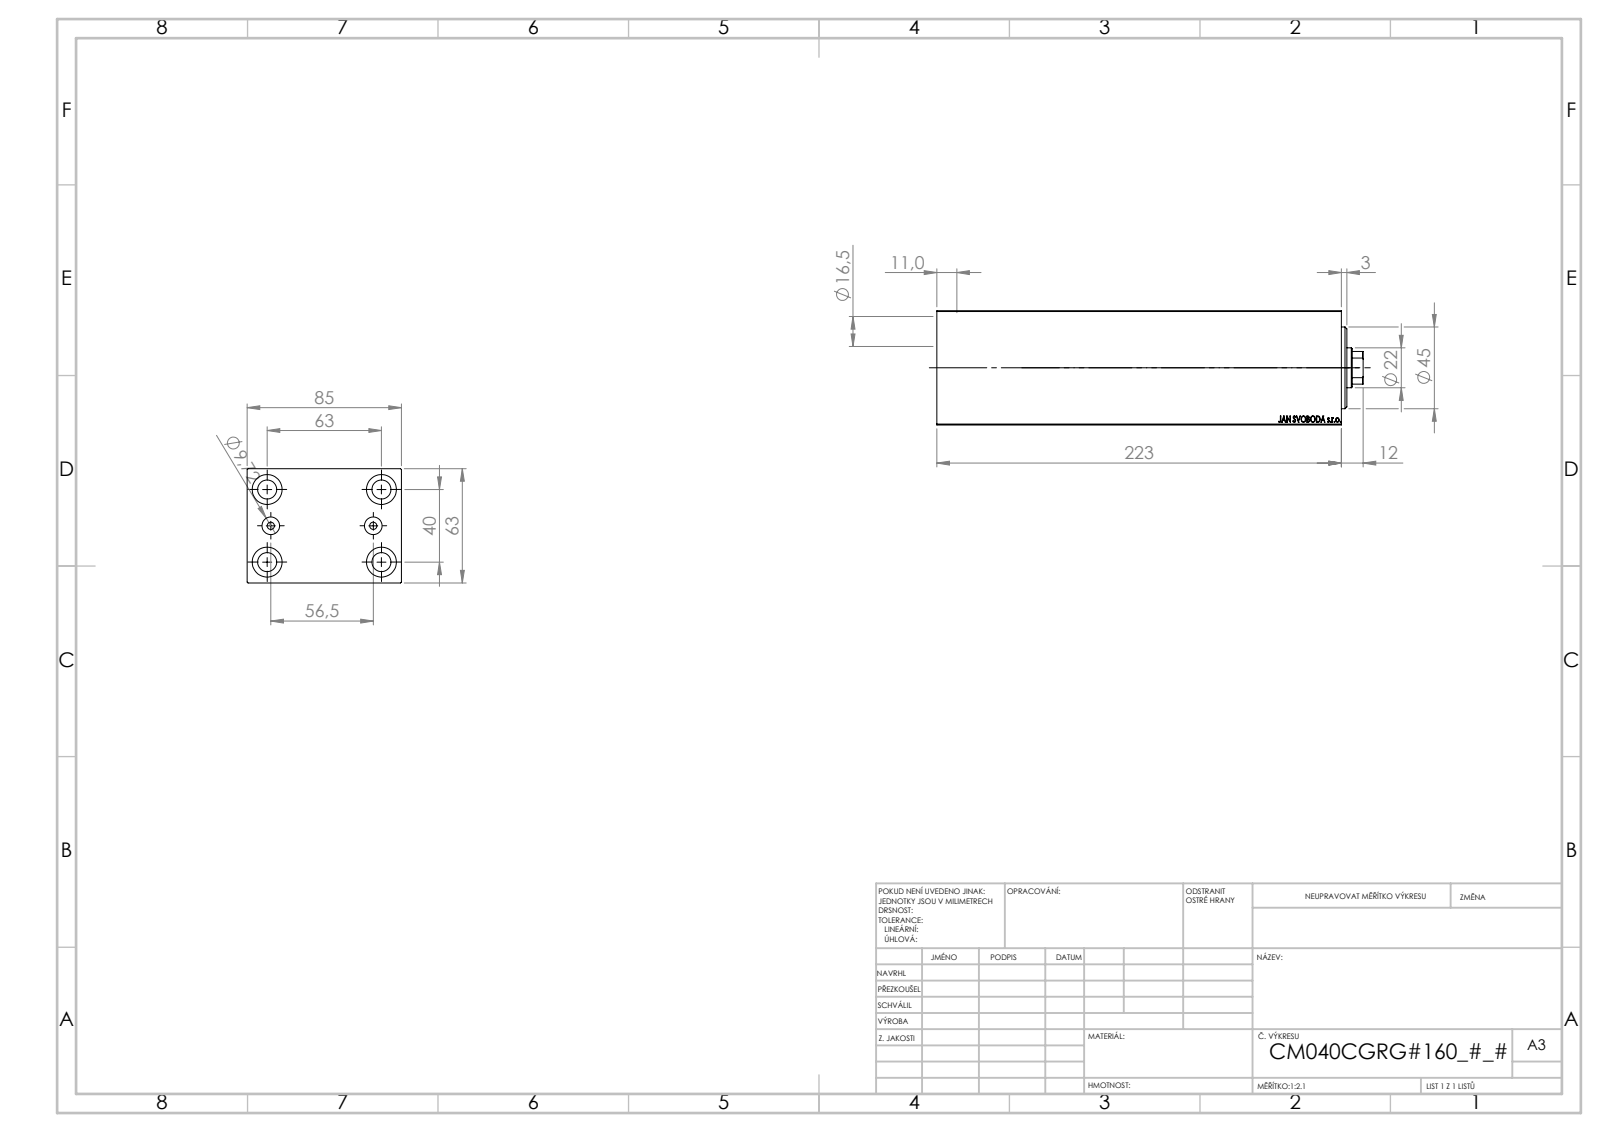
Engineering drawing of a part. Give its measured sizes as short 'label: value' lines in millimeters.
name: V450CM_C_Body; V450CM_C_VCP; V450CM_VC_B
written by: SolidWorks 2019 (CONFIG_CONTROL_DESIGN)
unit: mm
bodies: 3 solids, 858 faces (408 planar, 56 cylindrical, 394 other)
size: 234 × 85 × 63
volume: 1 095 000 mm³; area: 135 319 mm²
holes: 4× ⌀10.5, 4× ⌀16.5, 2× ⌀4, 2× ⌀9.72, 1× ⌀12.5, 1× ⌀22, 1× ⌀25.5, 1× ⌀40, 1× ⌀42, 1× ⌀45
rounds: 1× R10.5
face distances: 63, 85, 223, 51, 172, 11, 21.6, 29.4, 201.4, 10
hole spacings: 20.26, 37.31, 63.01, 28.25, 40, 63, 74.63, 56.5
